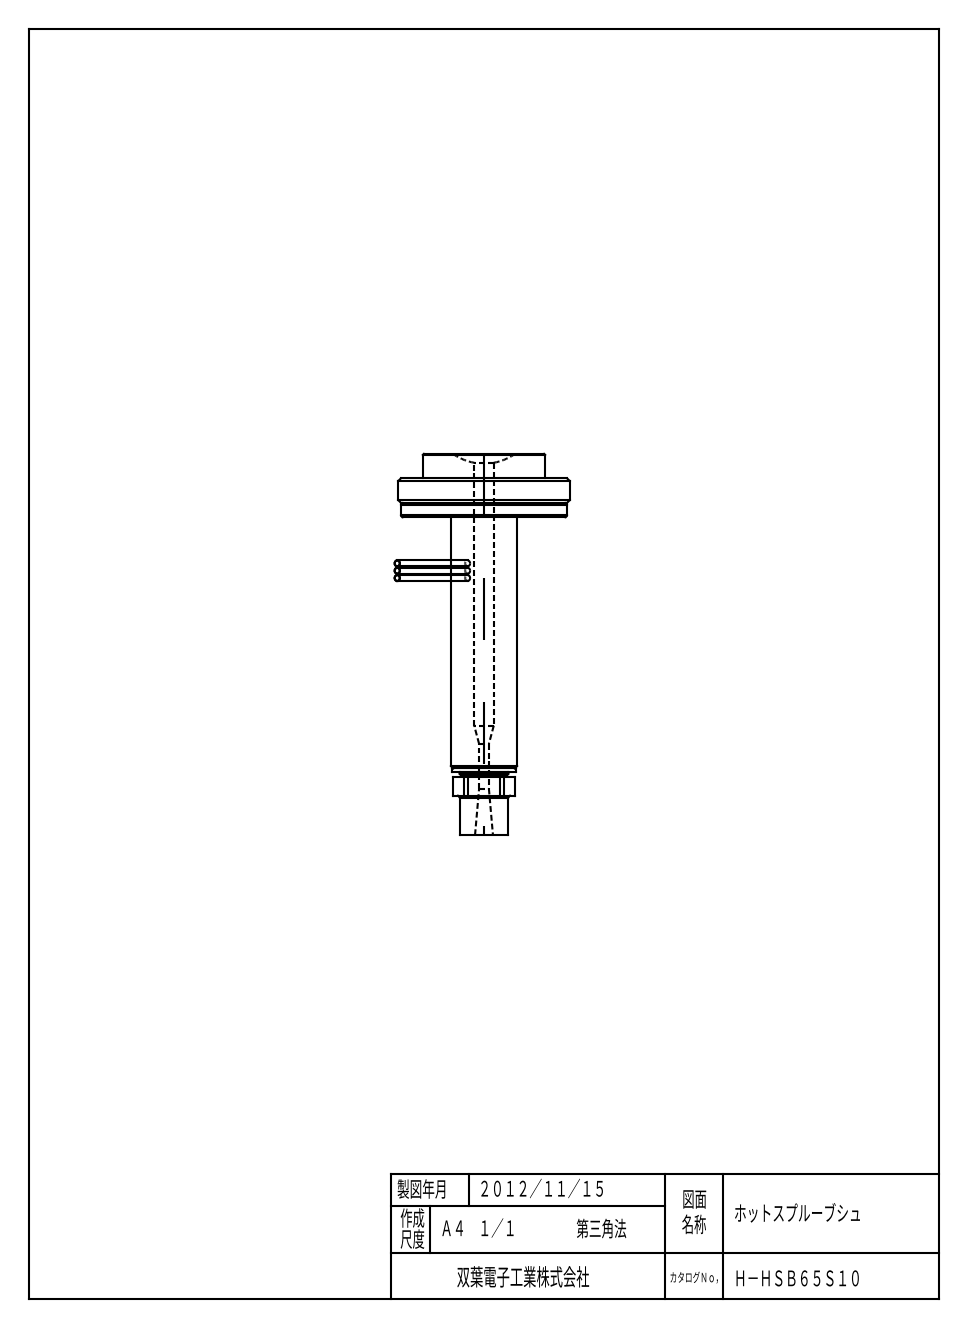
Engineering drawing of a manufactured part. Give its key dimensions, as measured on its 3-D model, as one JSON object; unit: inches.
{"part_name": "HSB65S10", "step_written_by": "SIEMENS PLM Software NX 2023 (AUTOMOTIVE_DESIGN)", "units": "inches", "bodies": {"solids": 1, "faces": 78, "planar": 27, "cylindrical": 28, "other": 23}, "overall_size": [6.313, 6.313, 3.071], "volume_in3": 1.064, "surface_area_in2": 14.51, "round_holes": [[0.217, 4], [0.35, 4], [0.157, 1], [0.63, 1]], "round_bosses_or_shafts": [[0.157, 3], [0.047, 3], [1.378, 1], [1.339, 1], [0.531, 1], [0.512, 1], [0.5, 1], [0.394, 1]], "partial_cylinders_radius": [[0.492, 1]], "face_to_face_distances": [0.197, 0.315, 0.512, 0.295, 0.02, 0.217, 0.118, 2.091, 2.386, 2.406], "hole_center_spacings": [0.492, 0.696, 0.984]}
